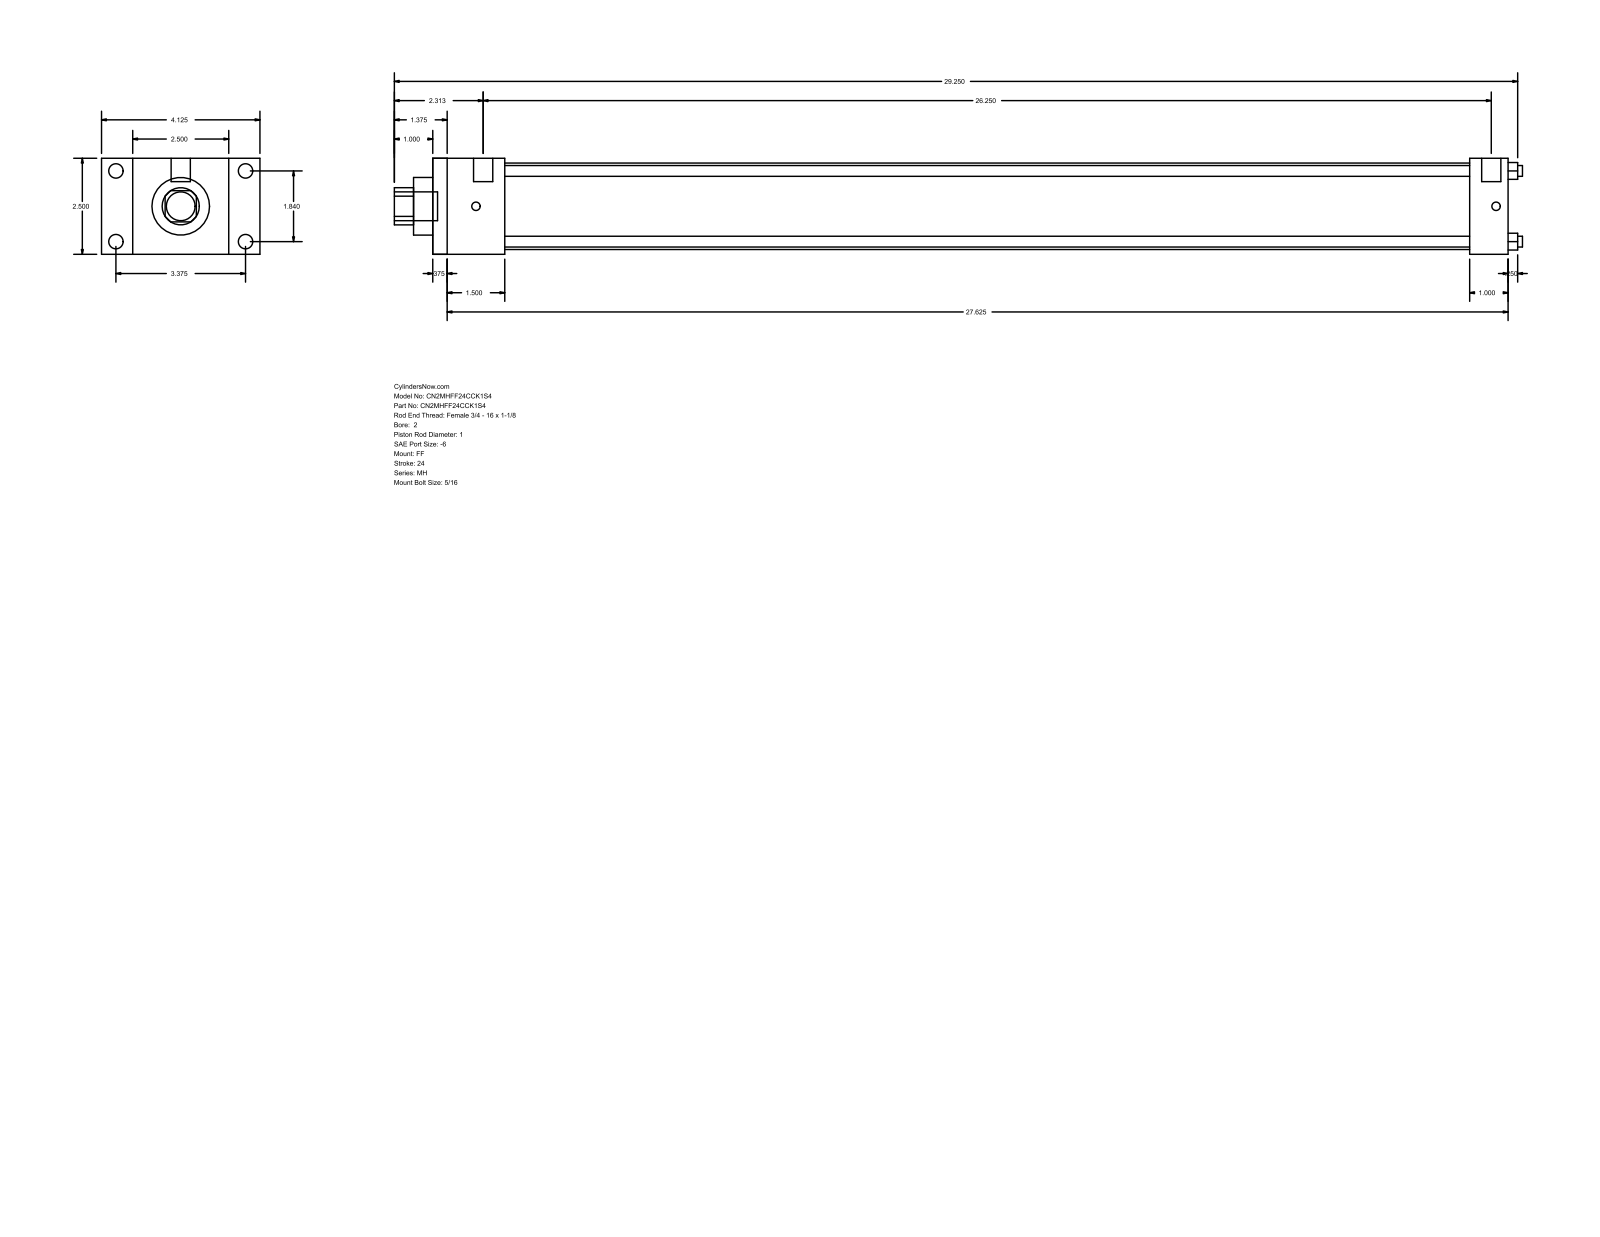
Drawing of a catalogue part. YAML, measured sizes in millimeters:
part_name: "MH_FF__0200_1"
step_written_by: "GSSL Pune (CONFIG_CONTROL_DESIGN)"
units: millimeters
bodies: {solids: 0, faces: 92, planar: 64, cylindrical: 28, other: 0}
overall_size: [746.12, 104.78, 63.5]
round_holes:
  - {diameter: 7.14, count: 4}
  - {diameter: 25.4, count: 1}
  - {diameter: 38.1, count: 1}
  - {diameter: 57.15, count: 1}
round_bosses_or_shafts:
  - {diameter: 9.53, count: 4}
  - {diameter: 5.56, count: 4}
  - {diameter: 12.7, count: 2}
  - {diameter: 19.05, count: 1}
partial_cylinders:
  - {radius: 12.29, count: 1}
face_to_face_distances: [63.5, 711.2, 9.52, 701.68, 20.64, 25.4, 47.63, 685.8, 38.11, 676.28]
hole_center_spacings: [33.05, 46.74, 66.1]
